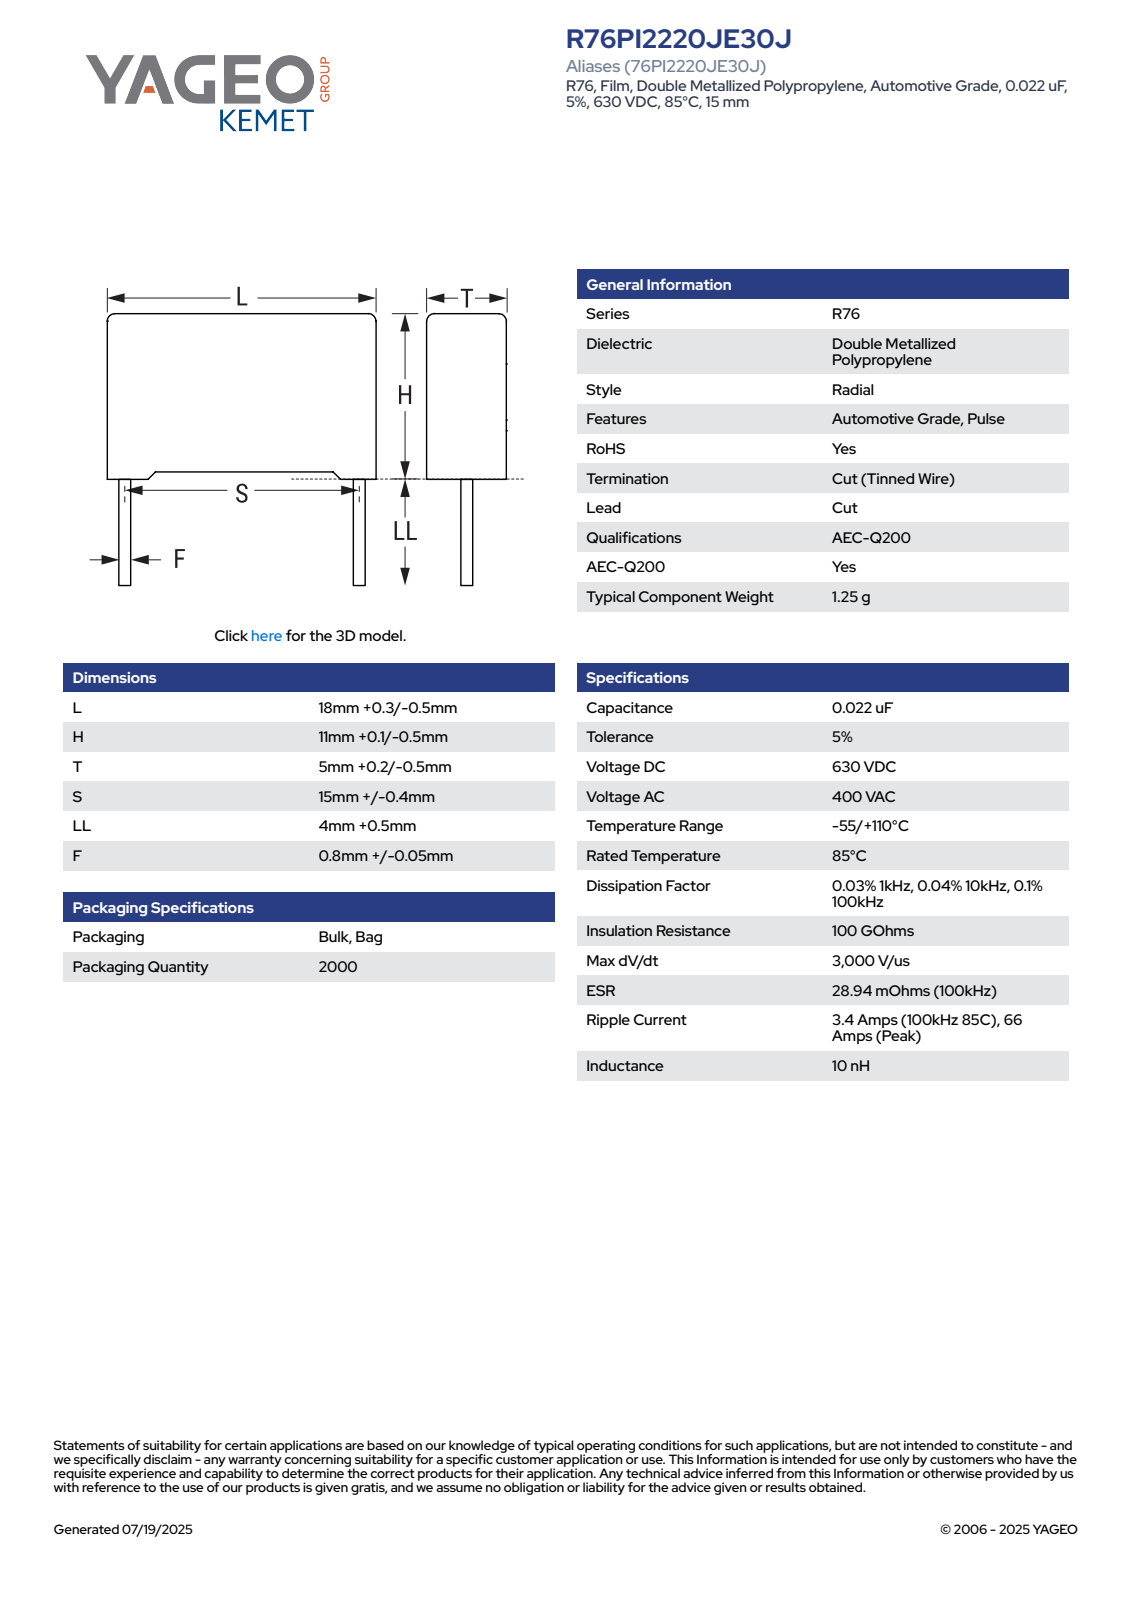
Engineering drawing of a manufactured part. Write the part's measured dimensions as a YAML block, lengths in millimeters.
part_name: "CFR_RB2_18X11X5_L18.3H11.1T5.2S15LL4.5F0.85"
step_written_by: "SolidWorks 2021 (AUTOMOTIVE_DESIGN)"
units: millimeters
bodies: {solids: 4, faces: 85, planar: 77, cylindrical: 8, other: 0}
overall_size: [18.3, 15.6, 5.21]
volume: 1003
surface_area: 769
round_bosses_or_shafts:
  - {diameter: 0.85, count: 2}
partial_cylinders:
  - {radius: 0.5, count: 4}
face_to_face_distances: [5.2, 10.35, 18.3, 0.61, 4.59, 0.37, 10.72, 0.38, 0.75, 11.1]
